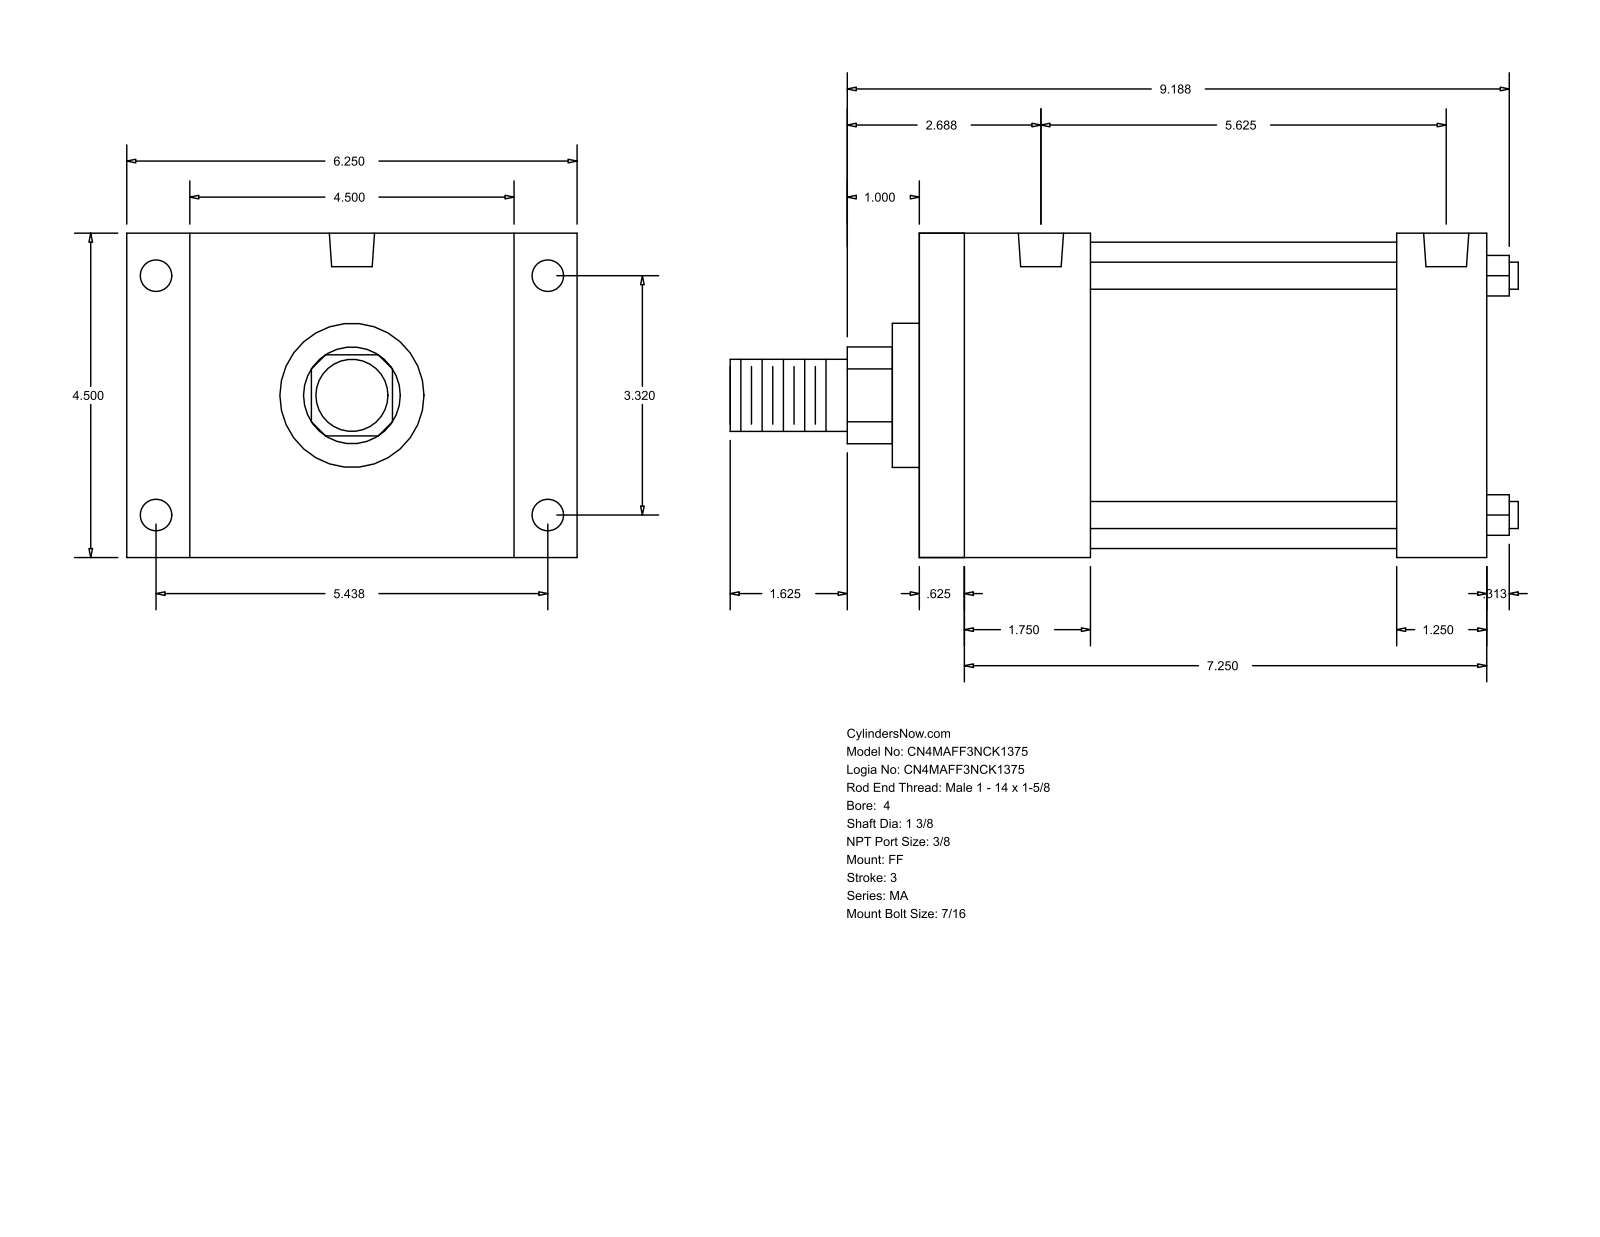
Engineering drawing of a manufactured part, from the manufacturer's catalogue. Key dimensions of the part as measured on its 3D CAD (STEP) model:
Part name (STEP PRODUCT): MA_FF__0400_1.375
STEP written by: GSSL Pune (CONFIG_CONTROL_DESIGN)
Units: millimetres
Bodies: 0 solids, 92 faces (64 planar, 28 cylindrical, 0 other)
Overall size (bounding box): 277.81 × 158.75 × 114.3
Round holes (diameter × count): ⌀11.11 ×8, ⌀15.93 ×2
Round bosses / shafts (diameter × count): ⌀9.53 ×4, ⌀107.95 ×1, ⌀50.8 ×1, ⌀34.92 ×1, ⌀25.4 ×1
Partial cylindrical surfaces — rounded edges, fillets, slot ends (radius × count): R17.06 ×1
Main face-to-face distances: 114.3, 200.03, 15.87, 184.16, 22.23, 136.53, 168.28, 152.41, 31.75, 60.32
Hole centre spacings: 138.12, 84.32, 133.35, 161.82, 4.76, 4.77, 138.11, 142.88
